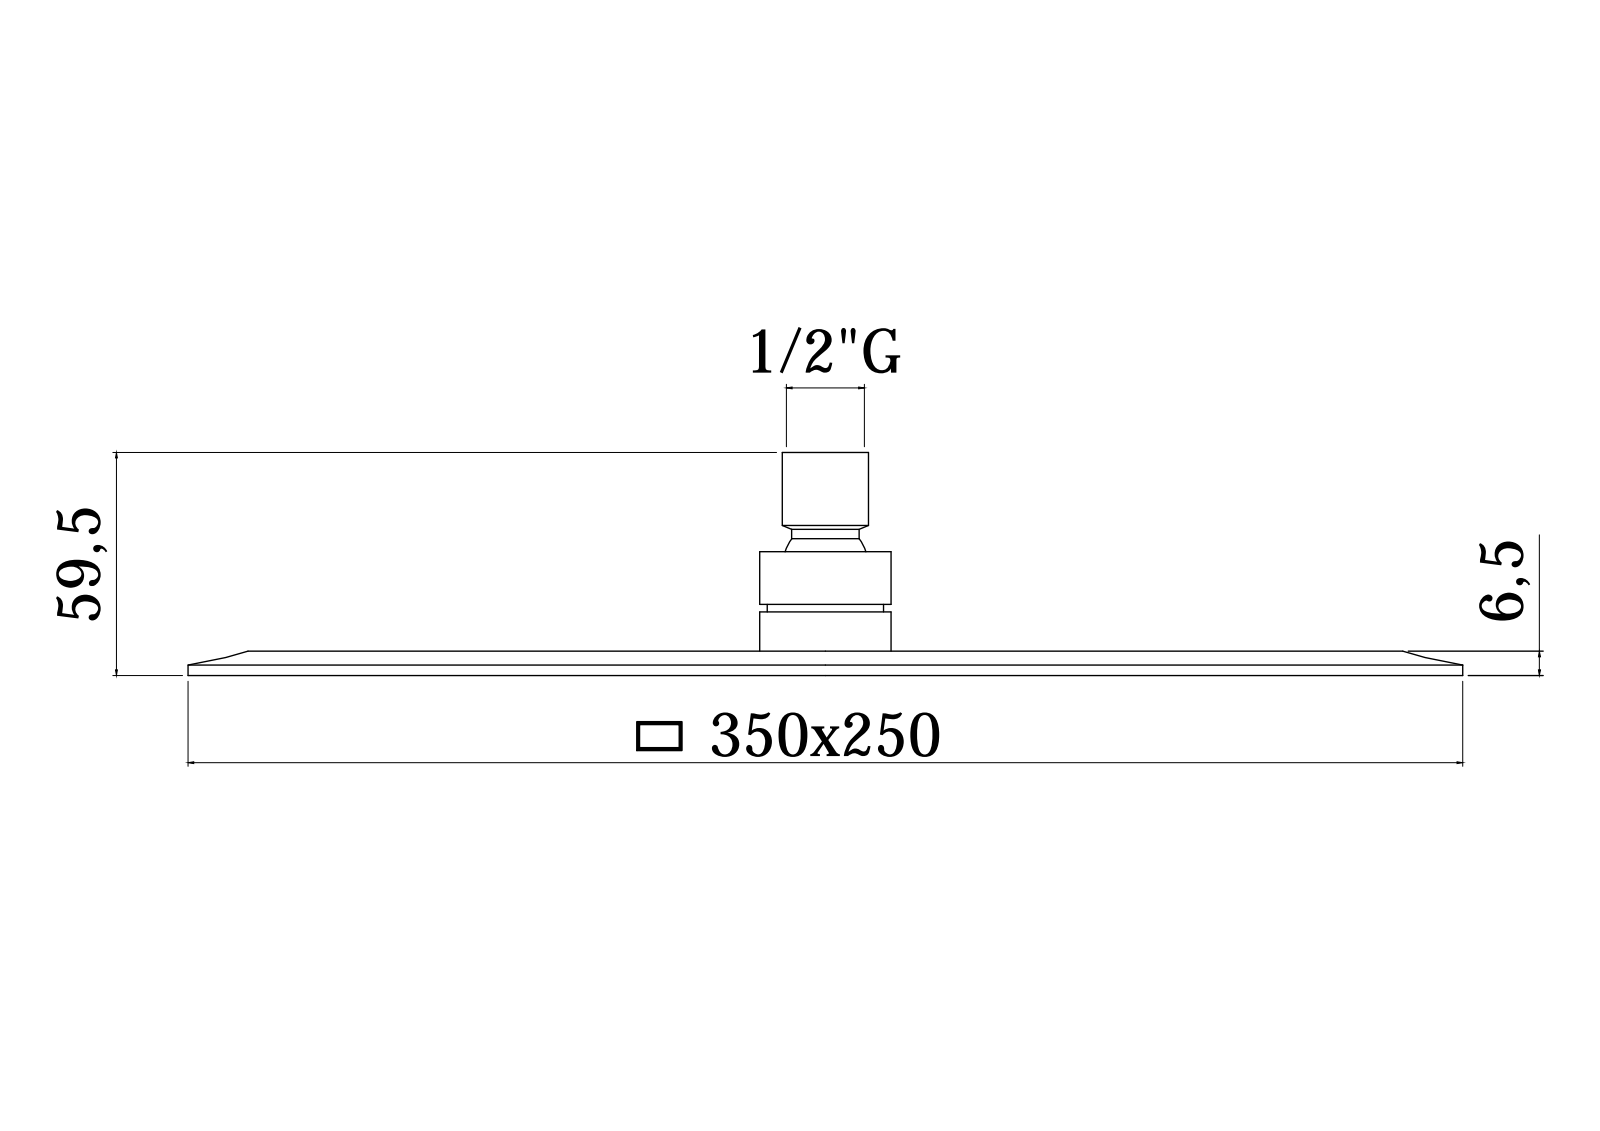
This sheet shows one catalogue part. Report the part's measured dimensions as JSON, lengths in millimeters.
{"part_name": "ZSOF102CR", "step_written_by": "CREO PARAMETRIC BY PTC INC, 2020044 (CONFIG_CONTROL_DESIGN)", "units": "millimeters", "bodies": {"solids": 1, "faces": 5299, "planar": 392, "cylindrical": 776, "other": 4131}, "overall_size": [350, 250, 48.9], "volume_mm3": 205111, "surface_area_mm2": 350968, "round_holes": [[1.5, 120], [1.7, 120], [7, 1], [15, 1], [16, 1], [16.5, 1], [18.63, 1], [23.8, 1], [24, 1], [26.5, 1], [28.1, 1], [28.2, 1]], "round_bosses_or_shafts": [[10, 120], [31.8, 1], [29.4, 1], [28, 1], [23.2, 1]], "partial_cylinders_radius": [[1, 16], [2, 12]], "face_to_face_distances": [1, 4, 3, 5, 2, 2.4, 2.6, 0.4, 1.4, 1.6], "hole_center_spacings": [34.83, 51.62, 71.31, 22, 44, 92.05, 66, 27]}
